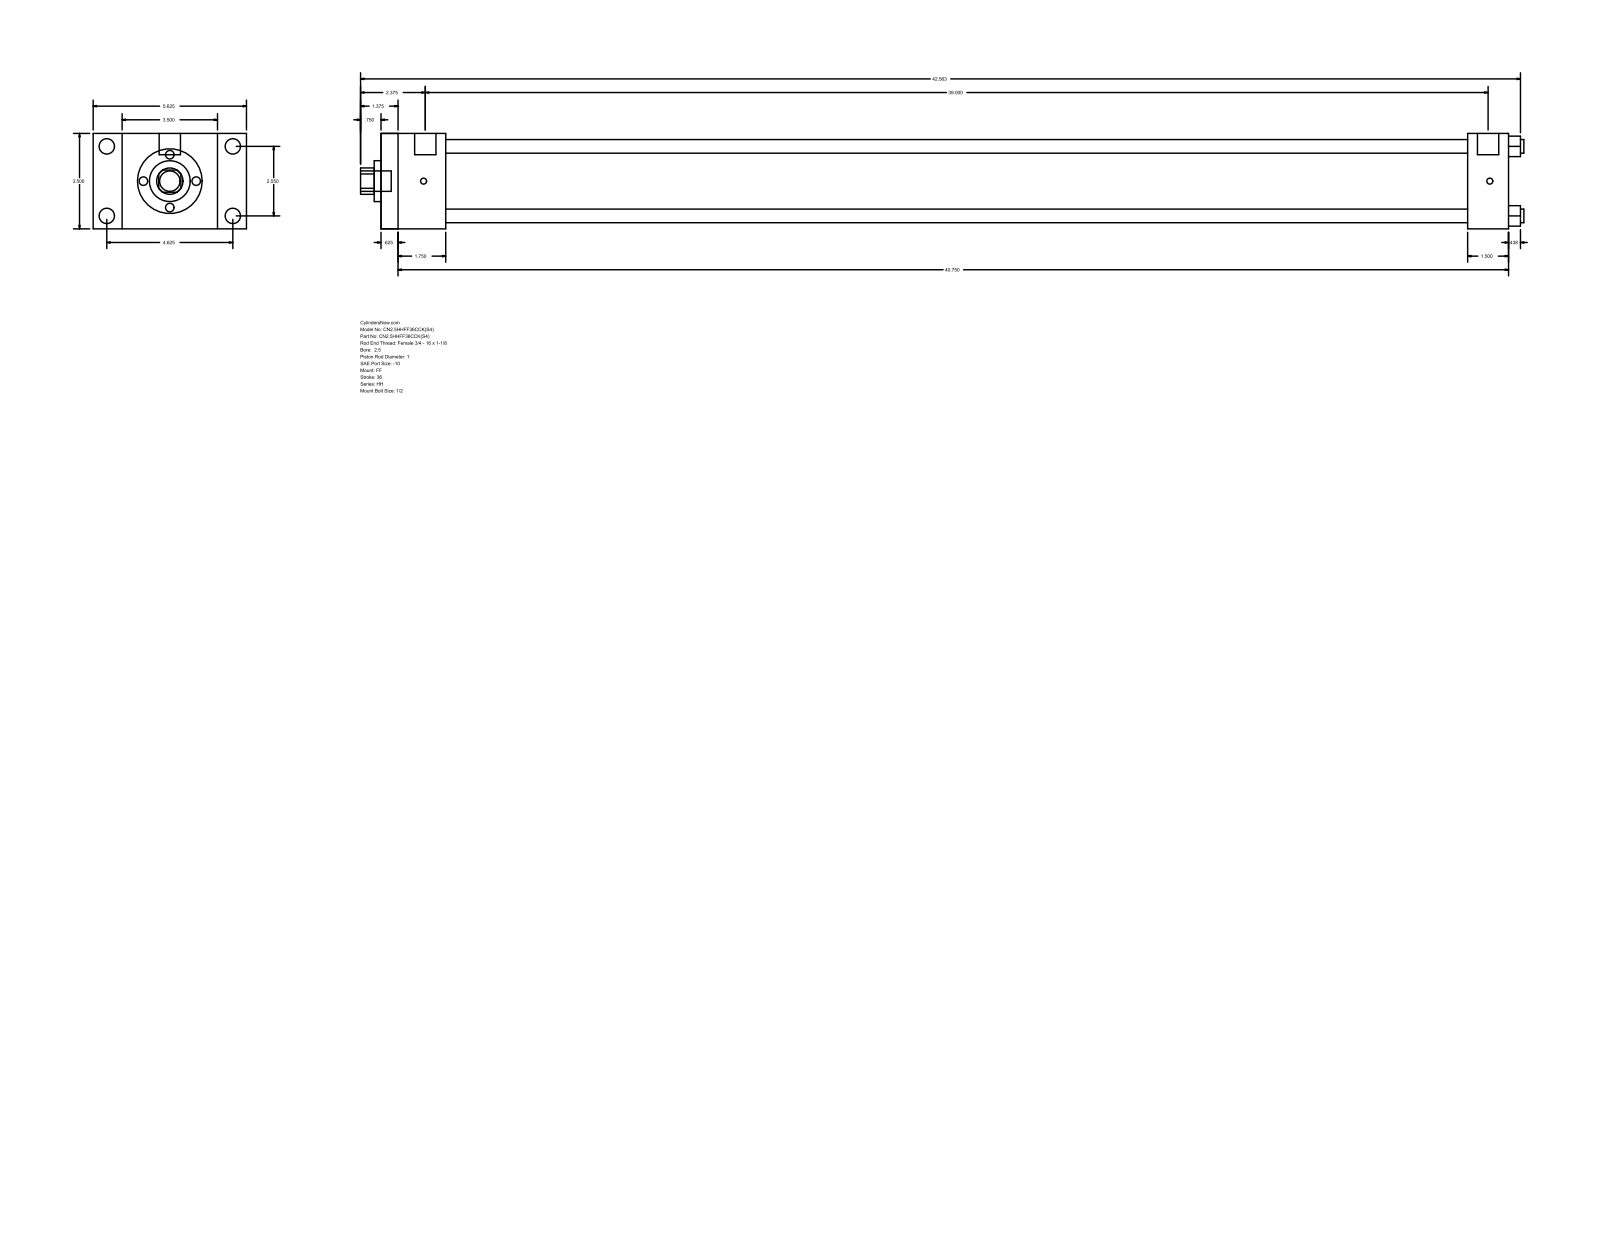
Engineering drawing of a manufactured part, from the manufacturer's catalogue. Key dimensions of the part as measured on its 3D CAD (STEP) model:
Part name (STEP PRODUCT): HH_FF__0250_1
STEP written by: GSSL Pune (CONFIG_CONTROL_DESIGN)
Units: millimetres
Bodies: 0 solids, 92 faces (64 planar, 28 cylindrical, 0 other)
Overall size (bounding box): 1084.26 × 142.88 × 88.9
Round holes (diameter × count): ⌀12.7 ×4, ⌀25.4 ×1, ⌀38.1 ×1, ⌀73.03 ×1
Round bosses / shafts (diameter × count): ⌀14.3 ×4, ⌀5.56 ×4, ⌀19.84 ×2, ⌀19.05 ×1
Partial cylindrical surfaces — rounded edges, fillets, slot ends (radius × count): R12.29 ×1
Main face-to-face distances: 88.9, 1050.92, 15.87, 1035.05, 60.33, 44.46, 990.59, 1012.83, 996.96, 952.5
Hole centre spacings: 45.79, 64.76, 91.58
